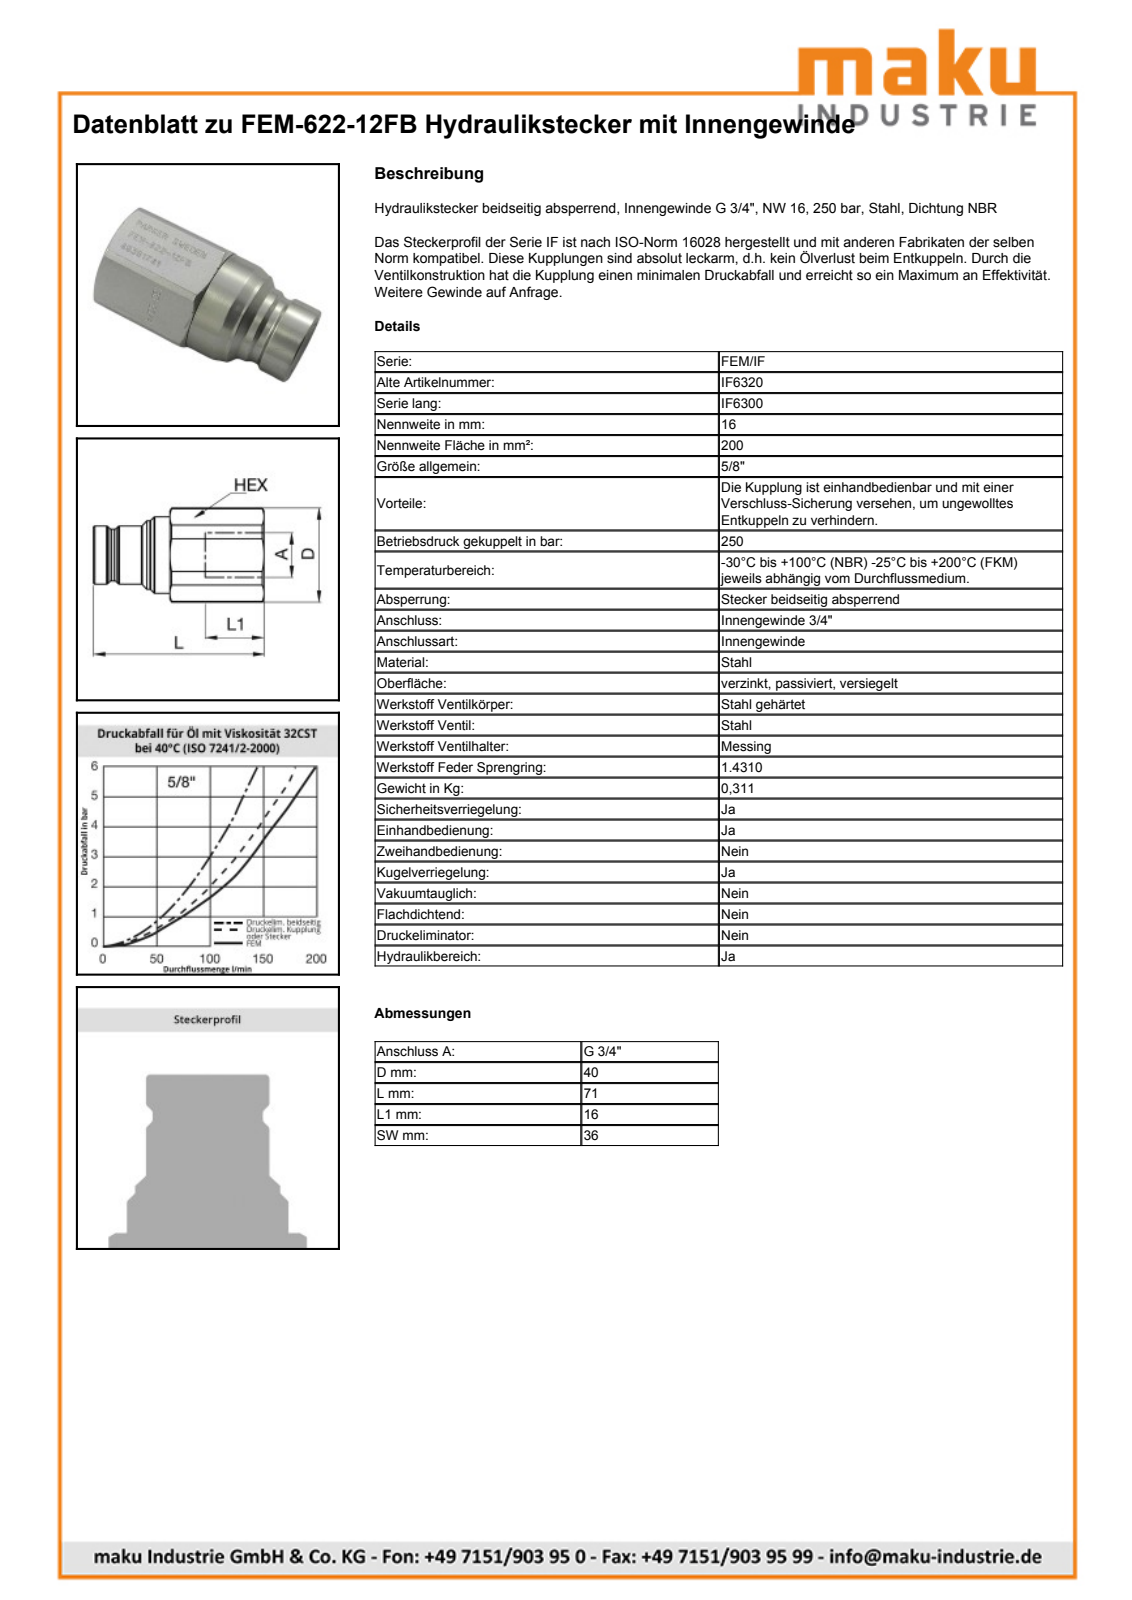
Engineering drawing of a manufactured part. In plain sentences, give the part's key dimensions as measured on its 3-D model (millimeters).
The part is named "FEM-622-12FB". Its 3-D file was written by "SolidWorks 2009 (AUTOMOTIVE_DESIGN)". It is 1 solid with 81 faces: 13 planar, 22 cylindrical and 46 other. Overall it measures 70.85 by 40 by 36 millimeters. Its volume is 56 370 cubic millimeters and its surface area 11 427 square millimeters. Round holes: 1 of diameter 17.65, 1 of diameter 24.12. Round bosses or shafts: 1 of diameter 35.5, 1 of diameter 32.95, 1 of diameter 27, 1 of diameter 24.5, 1 of diameter 17.5. Partial cylindrical surfaces (rounded edges, fillets, slot ends): 1 of radius 20. The main face-to-face distances are 36, 20.28, 50.57, 70.85, 50.51, 70.79, 34.85, 34.79, 15.72, 34.75.
